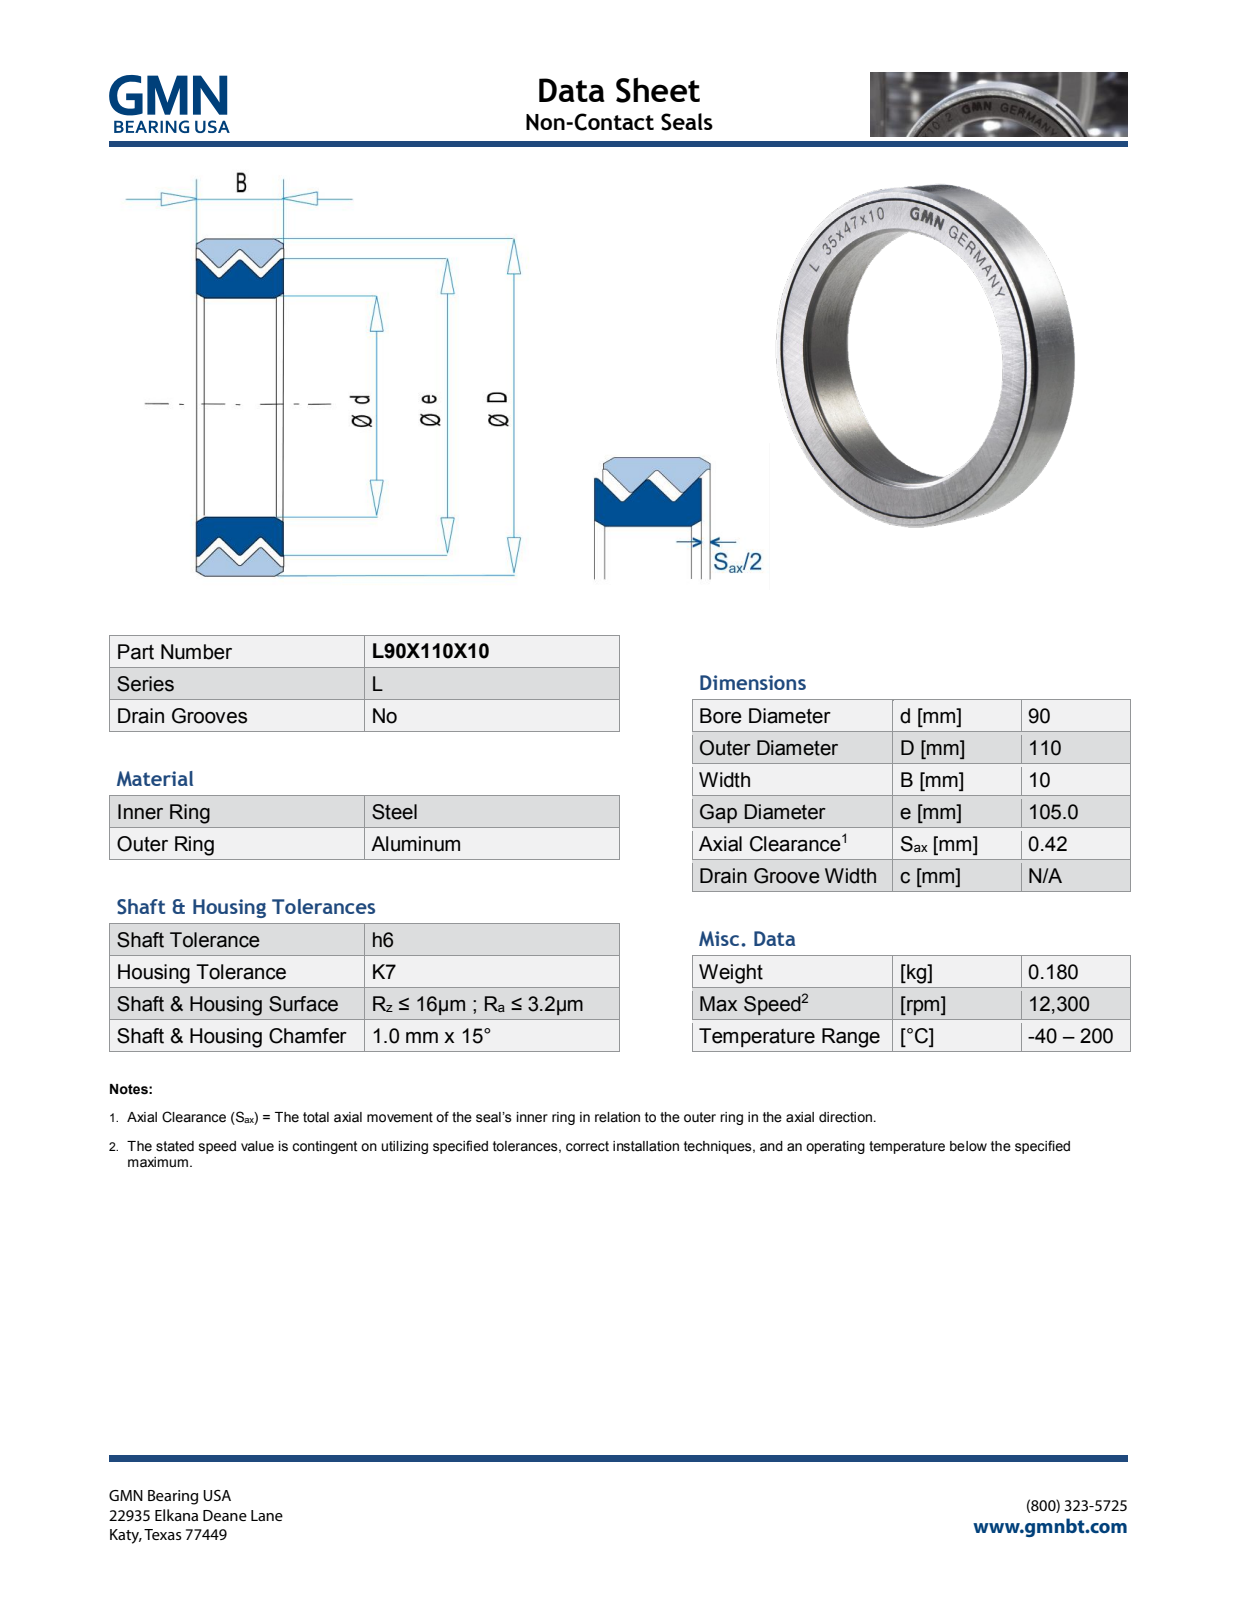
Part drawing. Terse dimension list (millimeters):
name: L90X110X10_PRT
written by: PRO/ENGINEER BY PARAMETRIC TECHNOLOGY CORPORATION, 2013150 (AUTOMOTIVE_DESIGN)
unit: mm
bodies: 2 solids, 591 faces (535 planar, 12 cylindrical, 44 other)
size: 110 × 110 × 10.07
volume: 30 422 mm³; area: 20 627 mm²
holes: 1× ⌀90, 1× ⌀105.3
bosses: 1× ⌀110, 1× ⌀105
face distances: 10, 10.07, 0.62, 4.93, 0.61, 4.31, 4.92, 0.63, 0.55, 3.69
